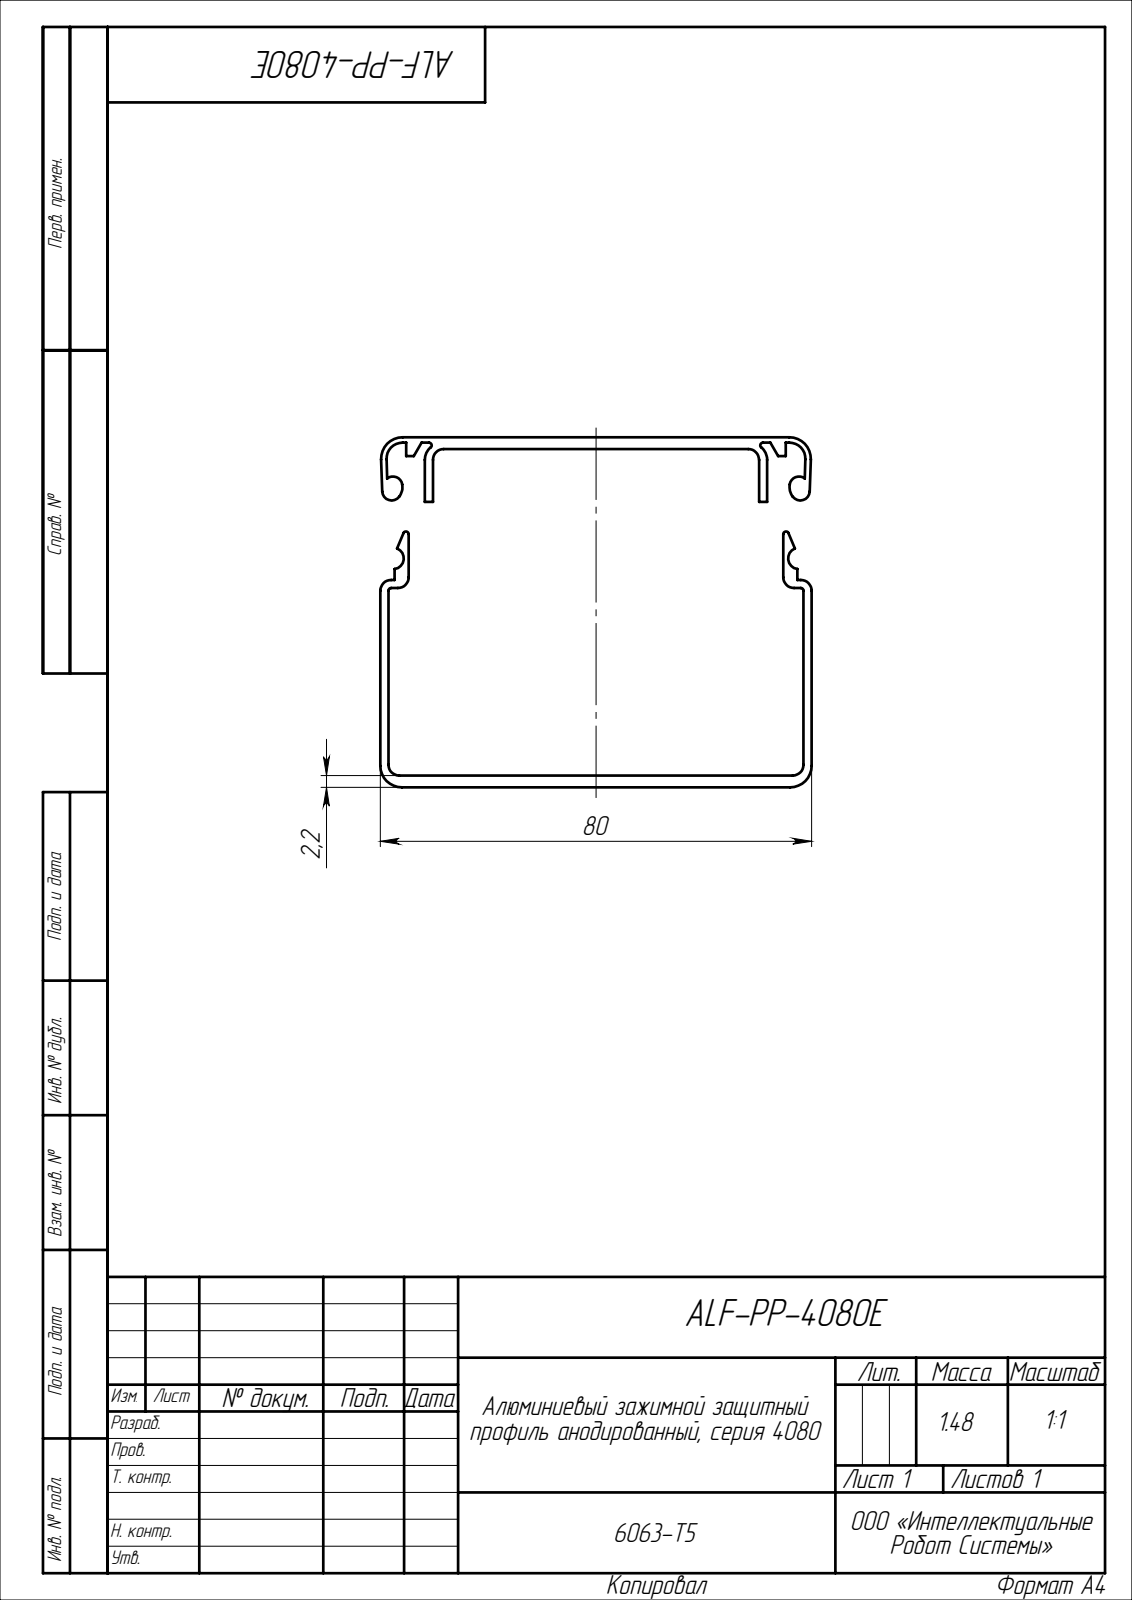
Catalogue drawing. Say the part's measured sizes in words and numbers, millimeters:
The part is named "ALF-PP-4040E_крышка^ALF-PP-4080E; ALF-PP-4040E_лоток^ALF-PP-4080E; ALF-PP-4080E". Its 3-D file was written by "SolidWorks 2022 (CONFIG_CONTROL_DESIGN)". It is 2 solids with 77 faces: 42 planar, 35 cylindrical and 0 other. Overall it measures 1000 by 80 by 65 millimeters. Its volume is 549 374 cubic millimeters and its surface area 608 037 square millimeters. Partial cylindrical surfaces (rounded edges, fillets, slot ends): 10 of radius 2, 6 of radius 0.5, 6 of radius 3, 4 of radius 1.75, 4 of radius 4. The main face-to-face distances are 2.2, 62.8, 65, 1.5, 78.5, 60.6, 80, 77, 8.25, 70.25.
